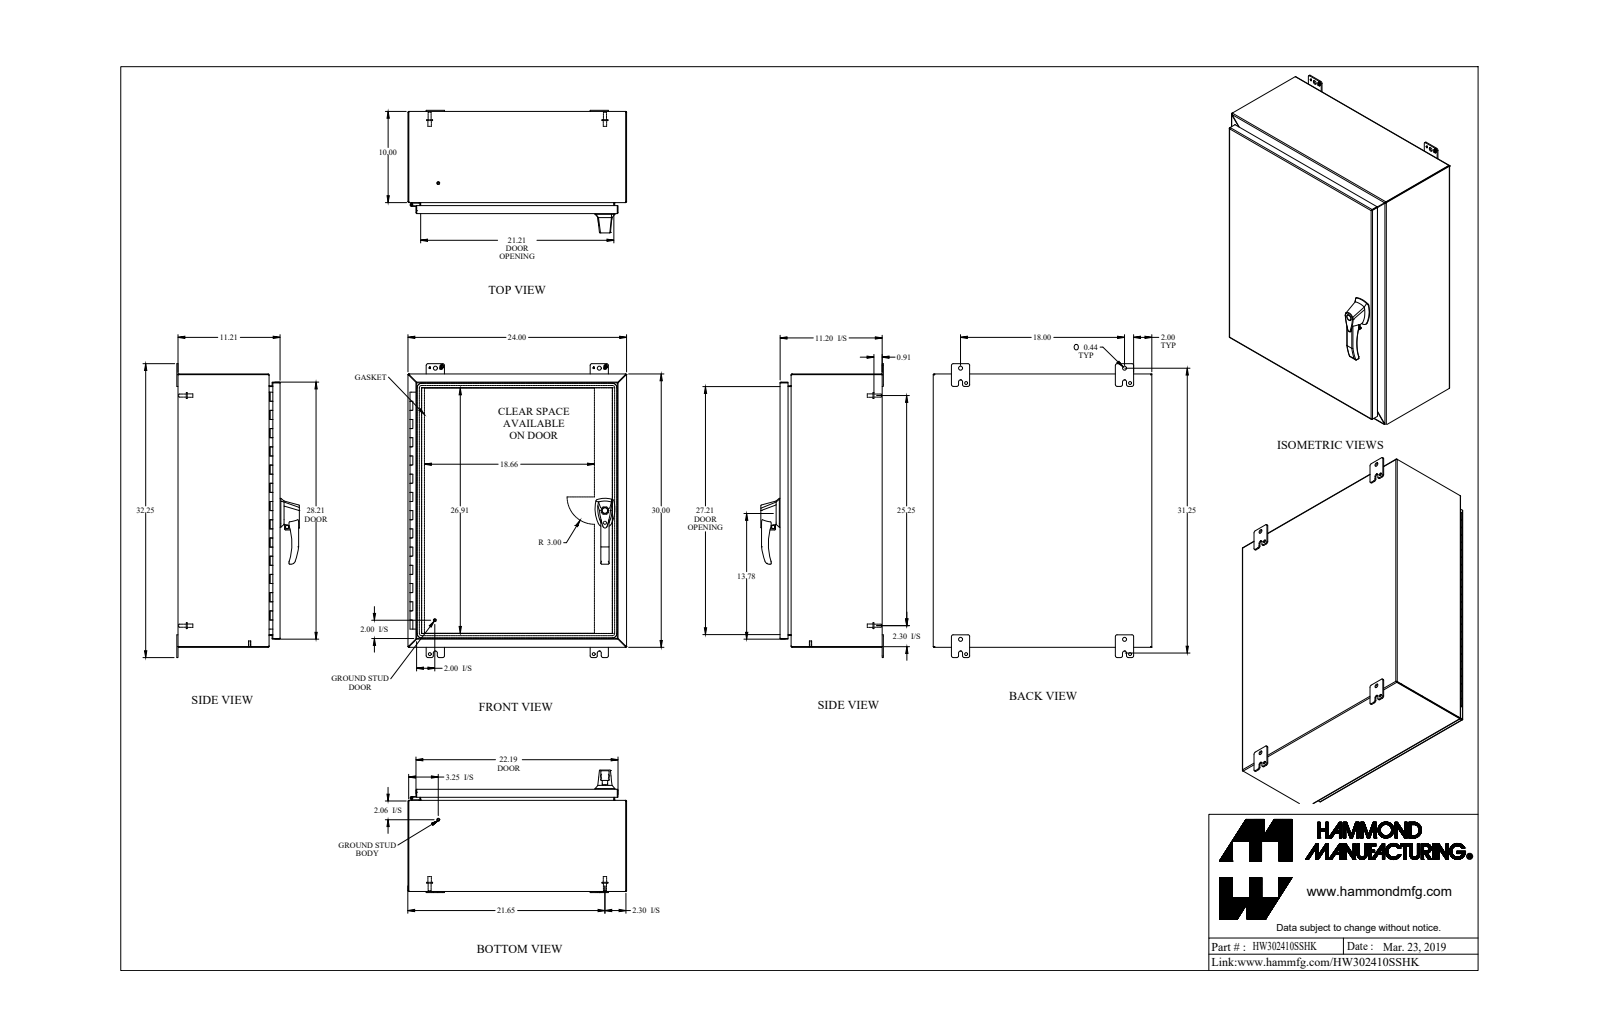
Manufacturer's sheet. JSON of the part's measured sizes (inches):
{"part_name": "HW302410SSHK", "step_written_by": "SolidWorks 2018 (AUTOMOTIVE_DESIGN)", "units": "inches", "bodies": {"solids": 42, "faces": 1458, "planar": 705, "cylindrical": 599, "other": 154}, "overall_size": [32.25, 24, 13.45], "volume_in3": 235.6, "surface_area_in2": 6127, "round_holes": [[0.176, 6], [0.313, 5], [0.25, 3], [0.265, 3], [0.413, 3], [0.196, 2], [0.256, 2], [0.394, 2], [0.437, 2], [0.187, 1], [0.233, 1], [0.33, 1]], "round_bosses_or_shafts": [[0.375, 9], [0.25, 7], [0.156, 6], [0.65, 4], [0.332, 4], [1, 3], [0.51, 3], [0.63, 2]], "partial_cylinders_radius": [[0.25, 27], [0.188, 24], [0.036, 20], [0.108, 20], [0.06, 12], [0.125, 9], [0.045, 8], [0.218, 8]], "face_to_face_distances": [0.072, 0.072, 11.138, 11.066, 11.138, 11.21, 23.928, 29.928, 23.856, 24], "hole_center_spacings": [1.11, 11.118, 11.119, 22.237, 11.119, 18, 23.752, 31.381]}
